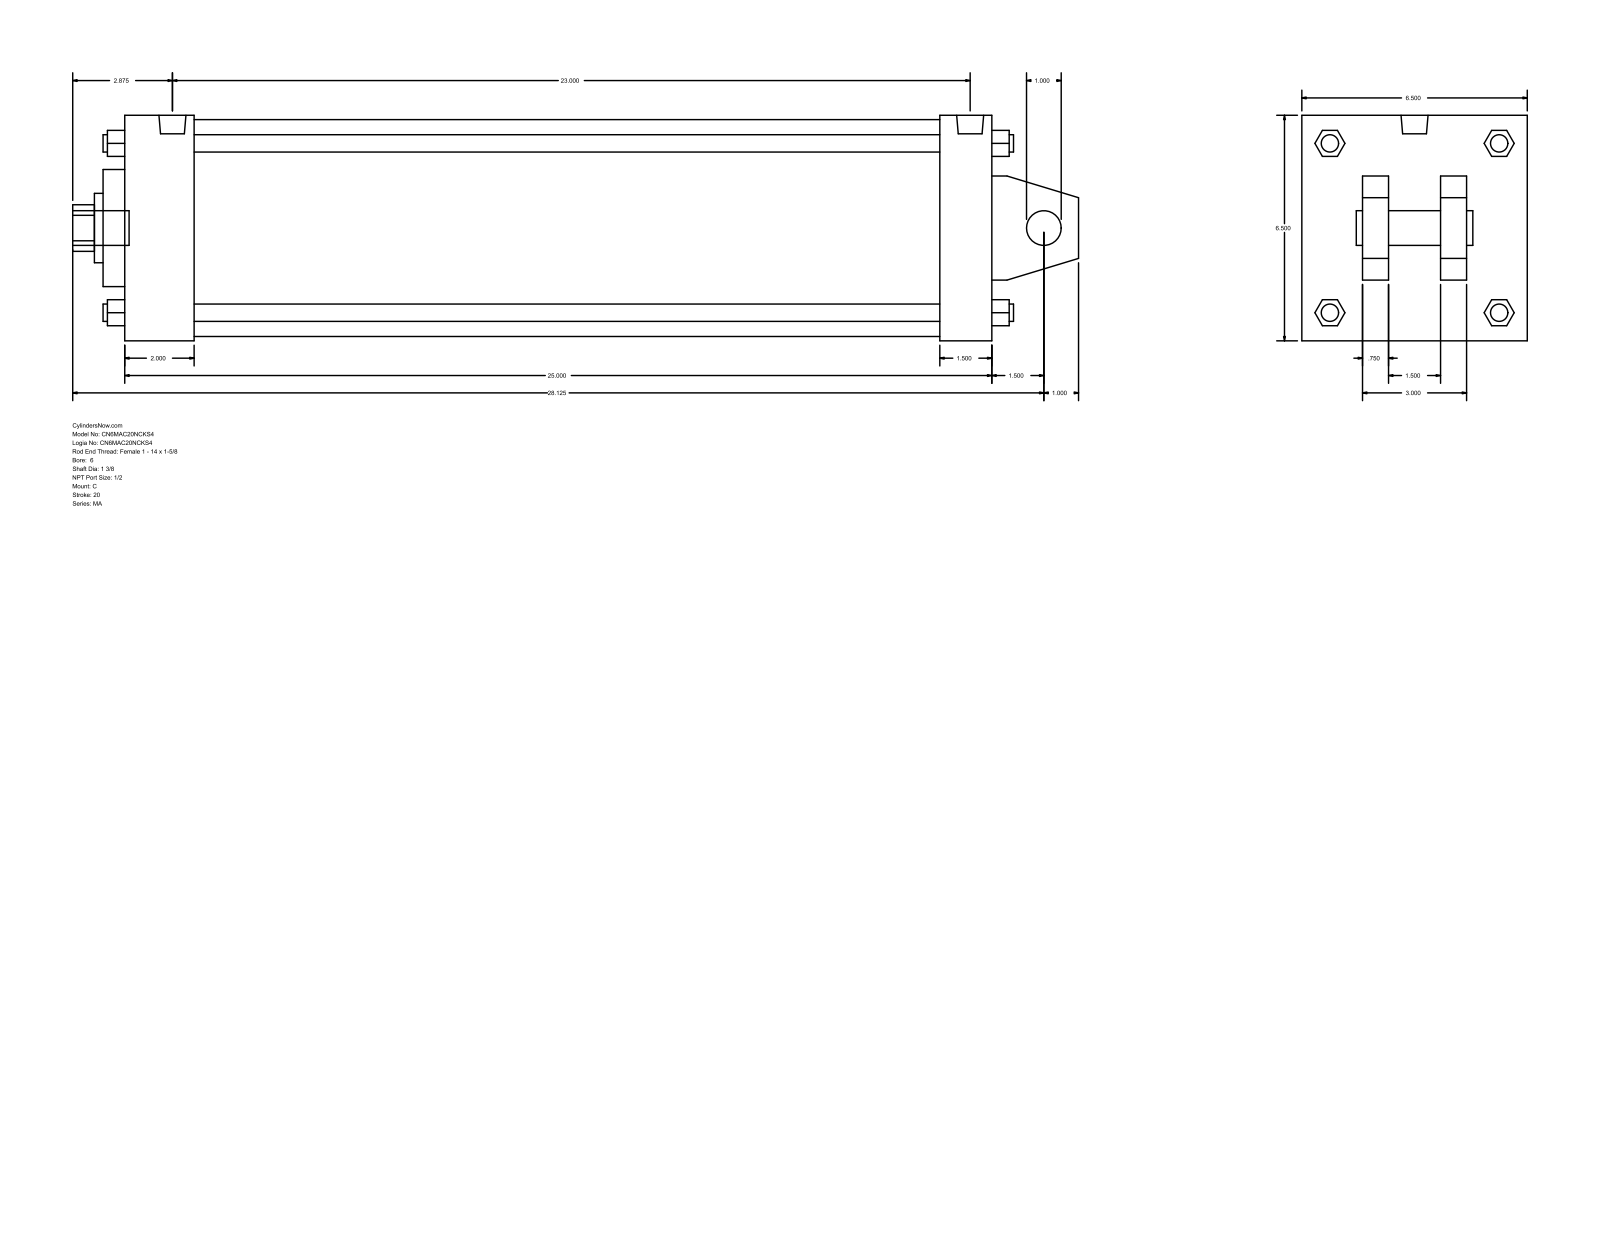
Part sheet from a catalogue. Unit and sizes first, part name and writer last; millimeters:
Units: millimetres
Overall size (bounding box): 736.6 × 165.1 × 165.1
Round holes (diameter × count): ⌀25.4 ×1, ⌀34.92 ×1, ⌀50.8 ×1, ⌀85.72 ×1, ⌀158.75 ×1
Round bosses / shafts (diameter × count): ⌀17.46 ×4, ⌀12.7 ×4, ⌀19.77 ×2, ⌀25.4 ×1
Partial cylindrical surfaces — rounded edges, fillets, slot ends (radius × count): R17.06 ×1
Main face-to-face distances: 165.1, 635, 38.1, 19.05, 63.5, 101.6, 50.8, 44.45, 120.65, 596.9
Bodies: 0 solids, 141 faces (109 planar, 32 cylindrical, 0 other)
Part name (STEP PRODUCT): MA_C__0600_1.375
STEP written by: GSSL Pune (CONFIG_CONTROL_DESIGN)
